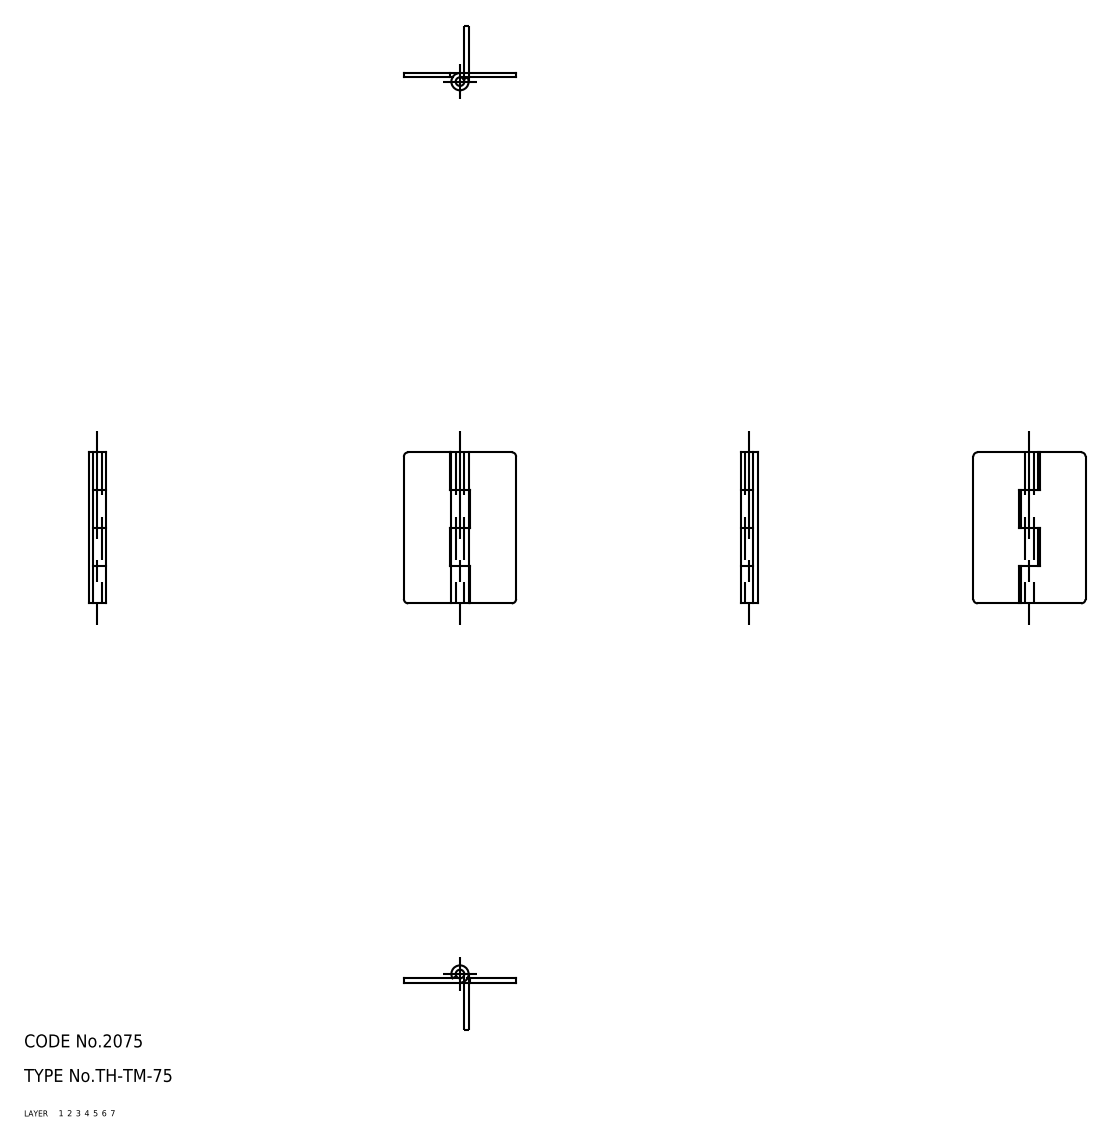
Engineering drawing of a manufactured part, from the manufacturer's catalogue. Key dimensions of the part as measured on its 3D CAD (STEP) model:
Part name (STEP PRODUCT): hinge piece_B; hinge piece_A; shaft; TH_TM_75_25413_36
STEP written by: CADfix (AUTOMOTIVE_DESIGN)
Units: millimetres
Bodies: 3 solids, 40 faces (0 planar, 0 cylindrical, 40 other)
Overall size (bounding box): 35 × 26 × 4
Volume: 1 209 mm³ · Surface area: 2 686 mm²
